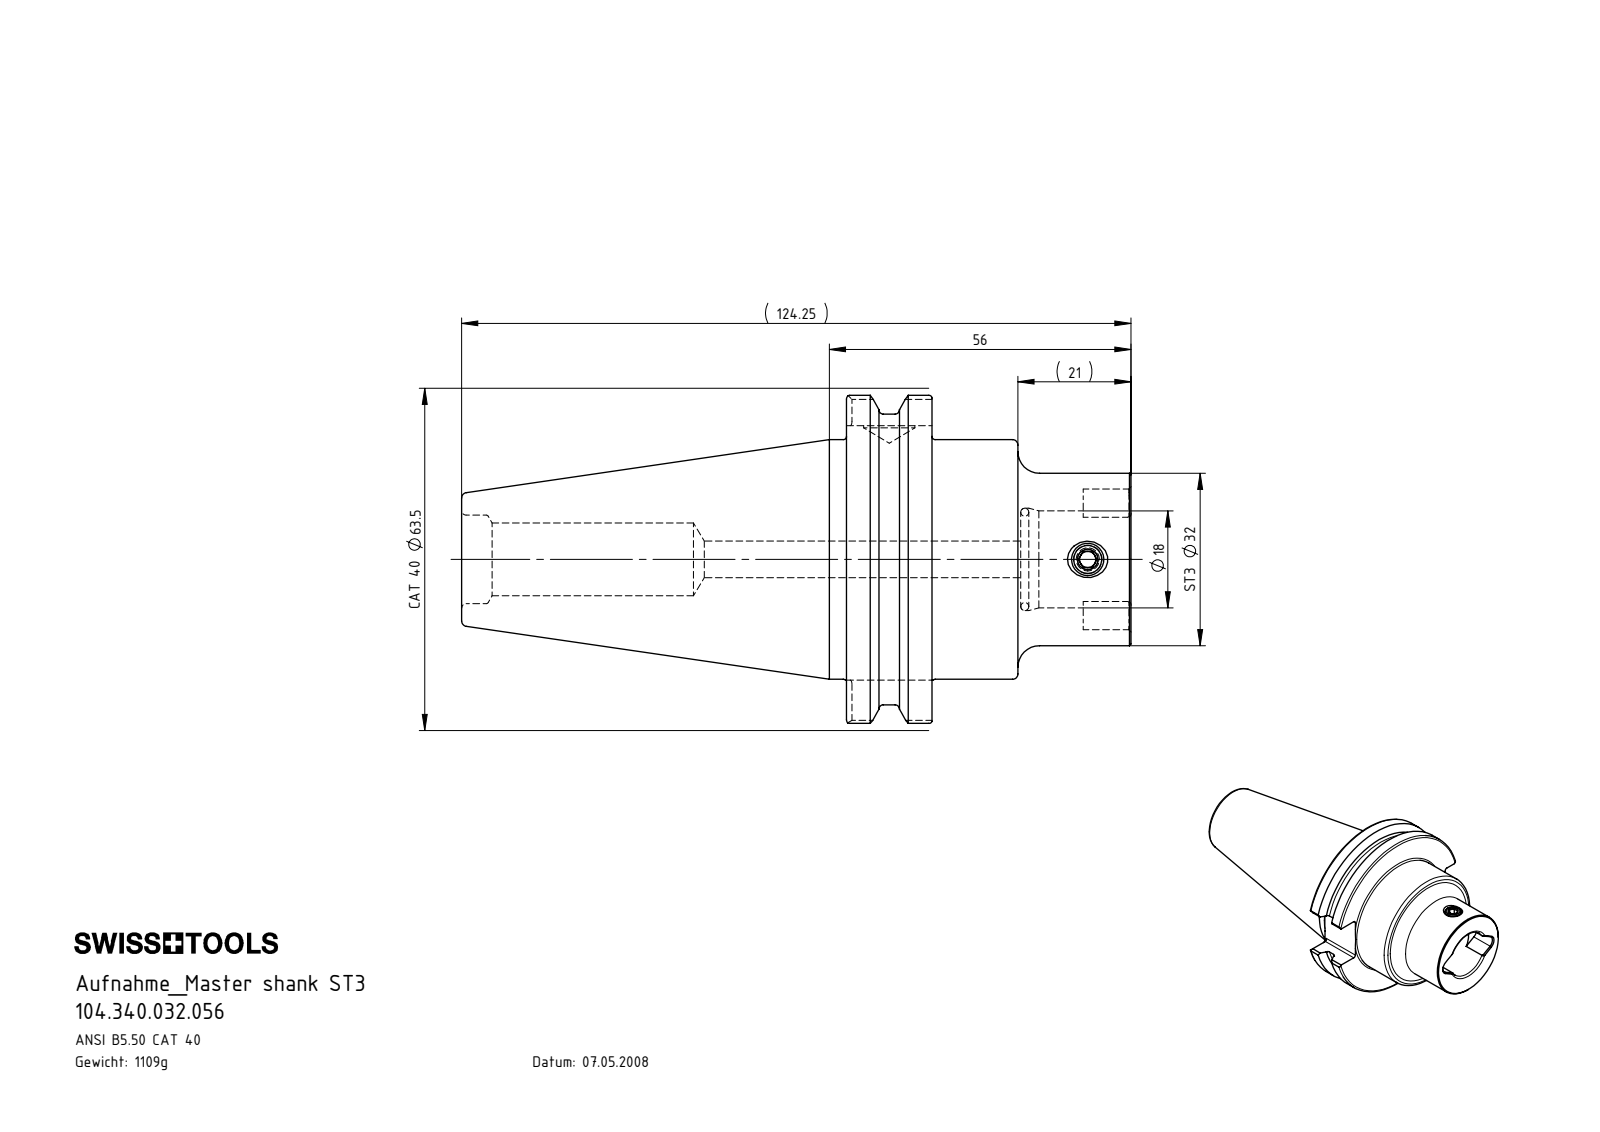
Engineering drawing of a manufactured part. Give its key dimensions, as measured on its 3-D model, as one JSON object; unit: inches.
{"part_name": "ST3-ER1.001.008_A; DIN 3771 - 16x1.5; CT4-ST3.K01.056_A; CT4-ST3.K01.056", "step_written_by": "SolidWorks 2015 (CONFIG_CONTROL_DESIGN)", "units": "inches", "bodies": {"solids": 3, "faces": 144, "planar": 44, "cylindrical": 39, "other": 61}, "overall_size": [4.892, 2.5, 2.396], "volume_in3": 8.626, "surface_area_in2": 39.43, "round_holes": [[0.207, 1], [0.268, 1], [0.374, 1], [0.531, 1], [0.647, 1], [0.709, 1], [0.748, 1]], "round_bosses_or_shafts": [[2.5, 1], [2.219, 1], [1.75, 1], [1.26, 1], [0.236, 1]], "partial_cylinders_radius": [[0.031, 8], [0.098, 2]], "face_to_face_distances": [0.625, 2.08, 1.455, 1.272, 0.648, 0.807, 1.858, 1.253, 0.628, 0.02]}
